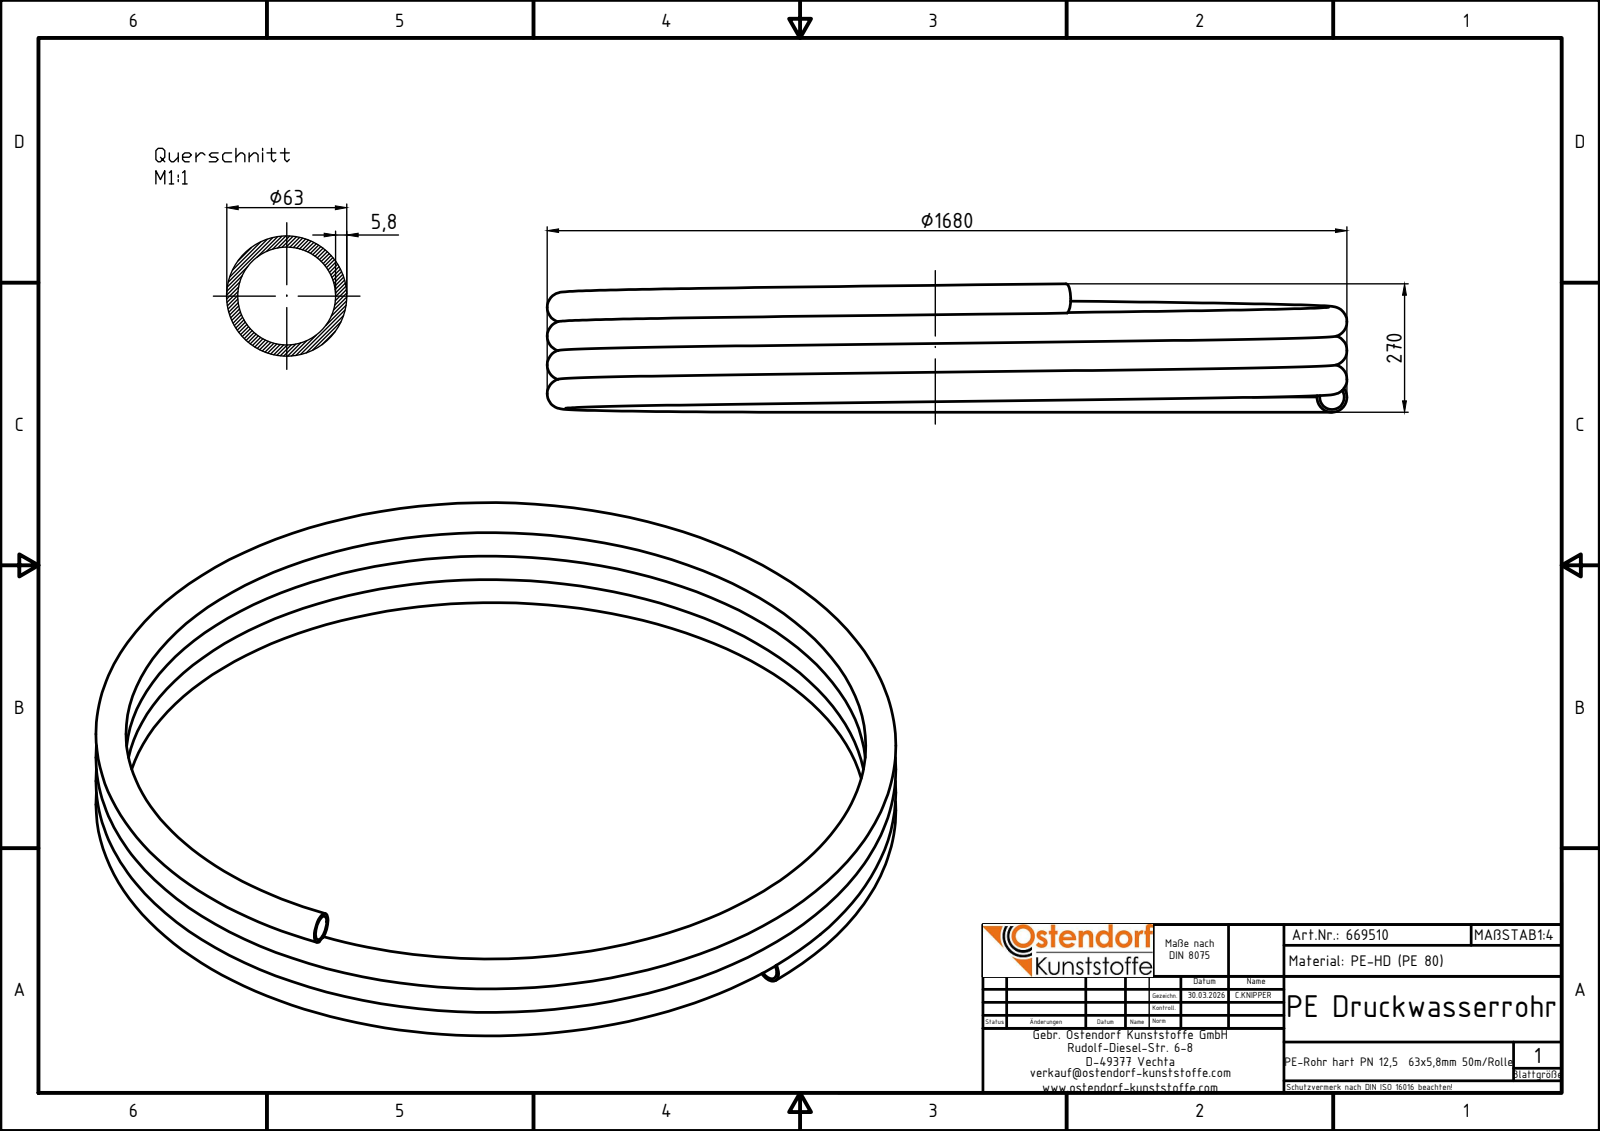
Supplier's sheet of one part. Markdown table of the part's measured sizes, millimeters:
| quantity | value |
| --- | --- |
| part name | 669510z |
| STEP written by | Autodesk Inventor 2024 (AUTOMOTIVE_DESIGN) |
| units | millimeters |
| bodies | 1 solid, 7 faces (3 planar, 0 cylindrical, 4 other) |
| overall size | 1680.01 × 1680.01 × 270.14 |
| volume | 19 090 000 mm³ |
| surface area | 6 281 000 mm² |
